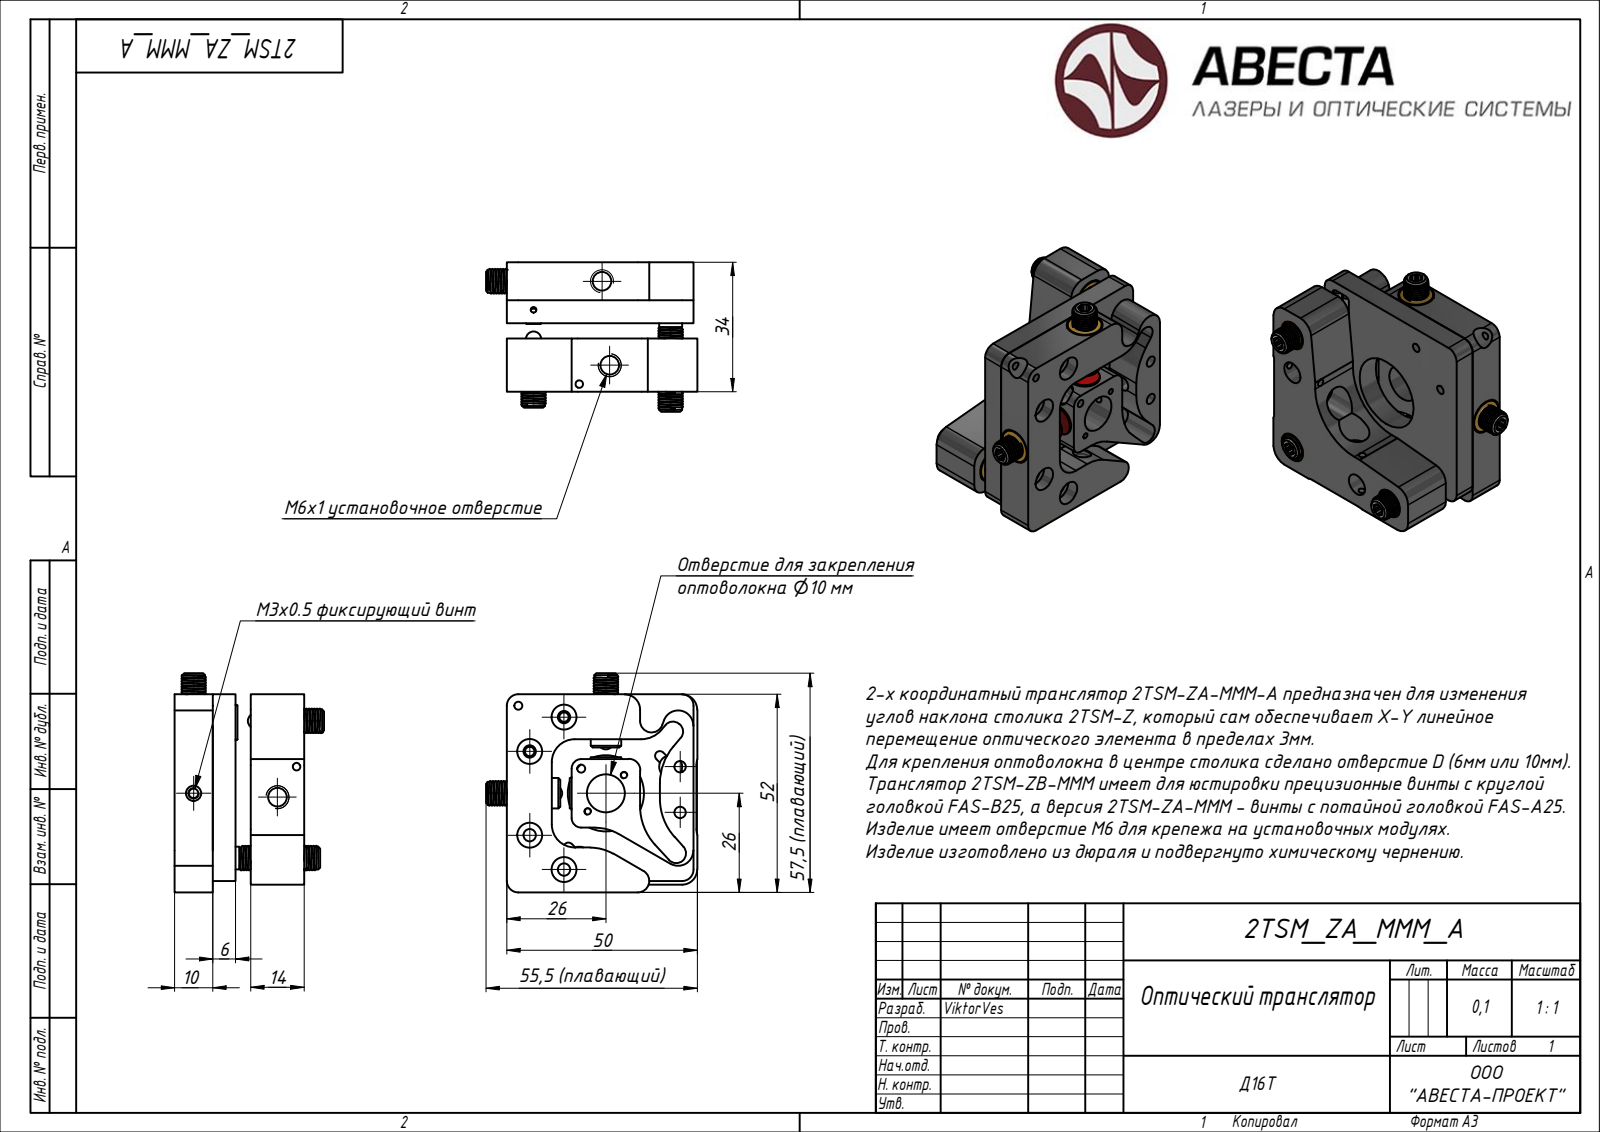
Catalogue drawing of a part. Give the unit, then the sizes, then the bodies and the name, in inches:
Units: inches
Overall size (bounding box): 2.264 × 2.106 × 1.545
Volume: 0.007 in³ · Surface area: 32.13 in²
Bodies: 7 solids, 544 faces (0 planar, 0 cylindrical, 544 other)
Part name (STEP PRODUCT): Block 02; Block 01
STEP written by: ST-DEVELOPER v15 (AUTOMOTIVE_DESIGN)
